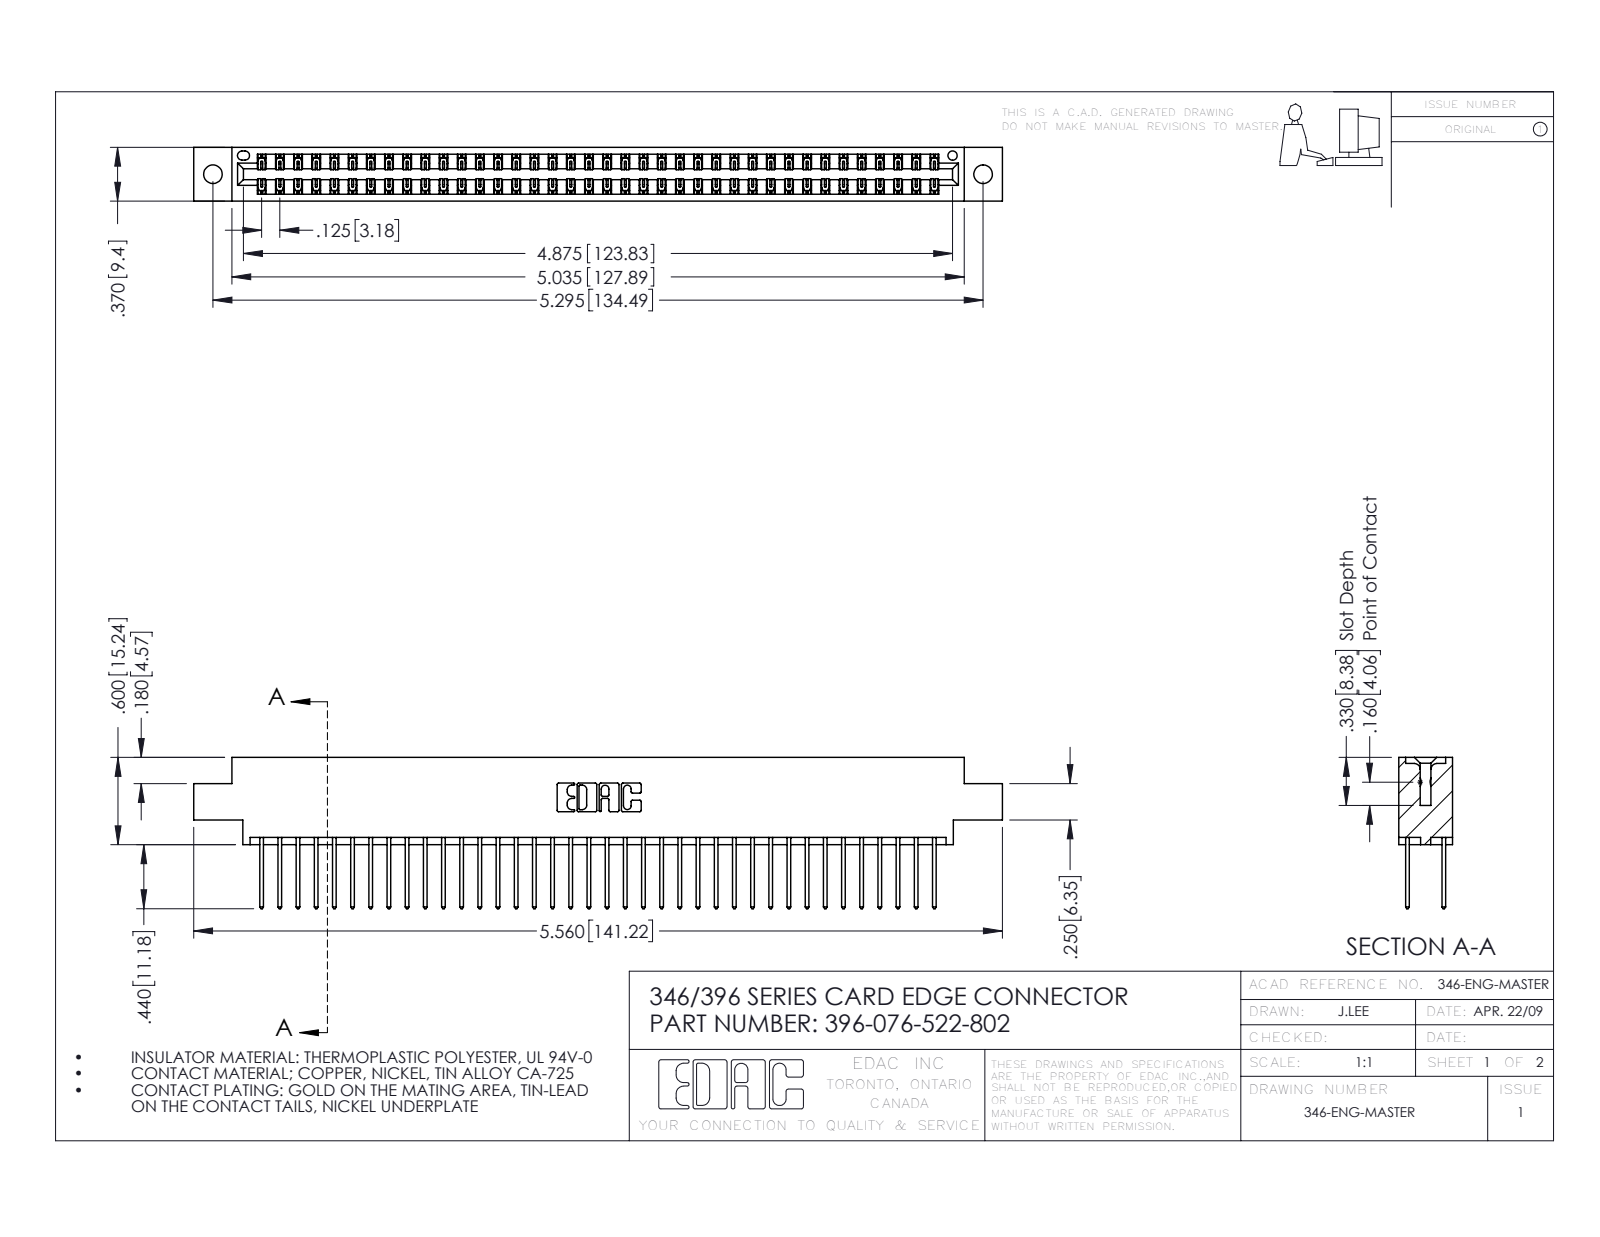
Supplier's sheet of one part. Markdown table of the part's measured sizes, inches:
| quantity | value |
| --- | --- |
| part name | 346 Part_0.170 Offset - 0.128 Dia; 345-292-001_345-293-122; 396-076-522-802 |
| STEP written by | SolidWorks 2016 (CONFIG_CONTROL_DESIGN) |
| units | inches |
| bodies | 77 solids, 4078 faces (2740 planar, 1338 cylindrical, 0 other) |
| overall size | 5.56 × 1.04 × 0.37 |
| volume | 0.839 in³ |
| surface area | 30.44 in² |
| round holes (diameter × count) | 0.128 × 2, 0.064 × 1 |
| partial cylindrical surfaces (radius × count) | 0.006 × 114, 0.01 × 76, 0.01 × 22, 0.007 × 6, 0.031 × 6, 0.026 × 3, 0.014 × 2, 0.022 × 2 |
| main face-to-face distances | 0.048, 0.322, 0.25, 0.37, 0.072, 0.298, 0.025, 0.275, 0.148, 0.222 |
| hole center spacings | 0.246, 5.086, 5.295 |
